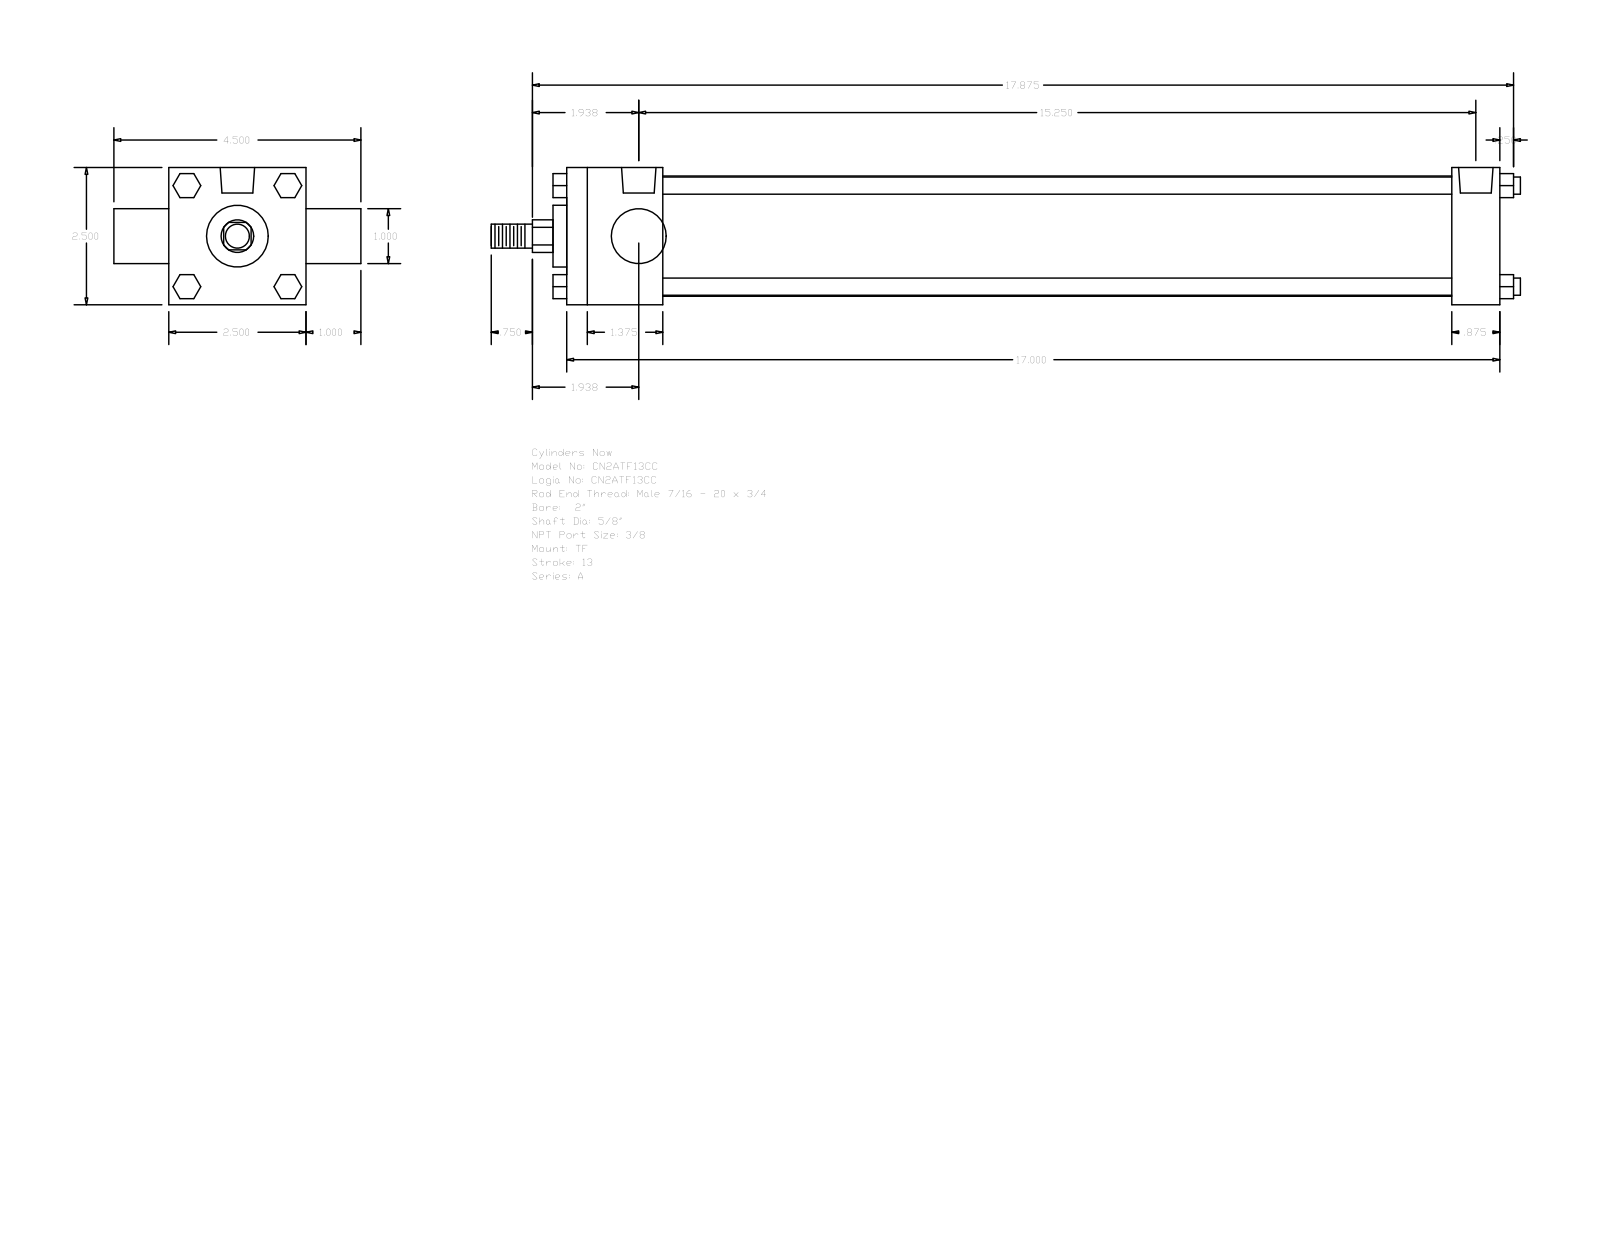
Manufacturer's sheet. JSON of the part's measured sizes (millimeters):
{"part_name": "A_TF__0200_0.625", "step_written_by": "GSSL Pune (CONFIG_CONTROL_DESIGN)", "units": "millimeters", "bodies": {"solids": 0, "faces": 120, "planar": 92, "cylindrical": 28, "other": 0}, "overall_size": [476.25, 114.3, 63.5], "round_holes": [[5.56, 3], [15.93, 2]], "round_bosses_or_shafts": [[7.94, 4], [55.63, 1], [28.57, 1], [25.4, 1], [15.88, 1], [11.11, 1]], "partial_cylinders_radius": [[7.54, 1]], "face_to_face_distances": [63.5, 431.8, 44.45, 409.57, 365.12, 387.35, 22.23, 25.4, 88.9, 50.8], "hole_center_spacings": [3.97, 3.98, 379.4, 383.37, 383.38, 387.35]}
